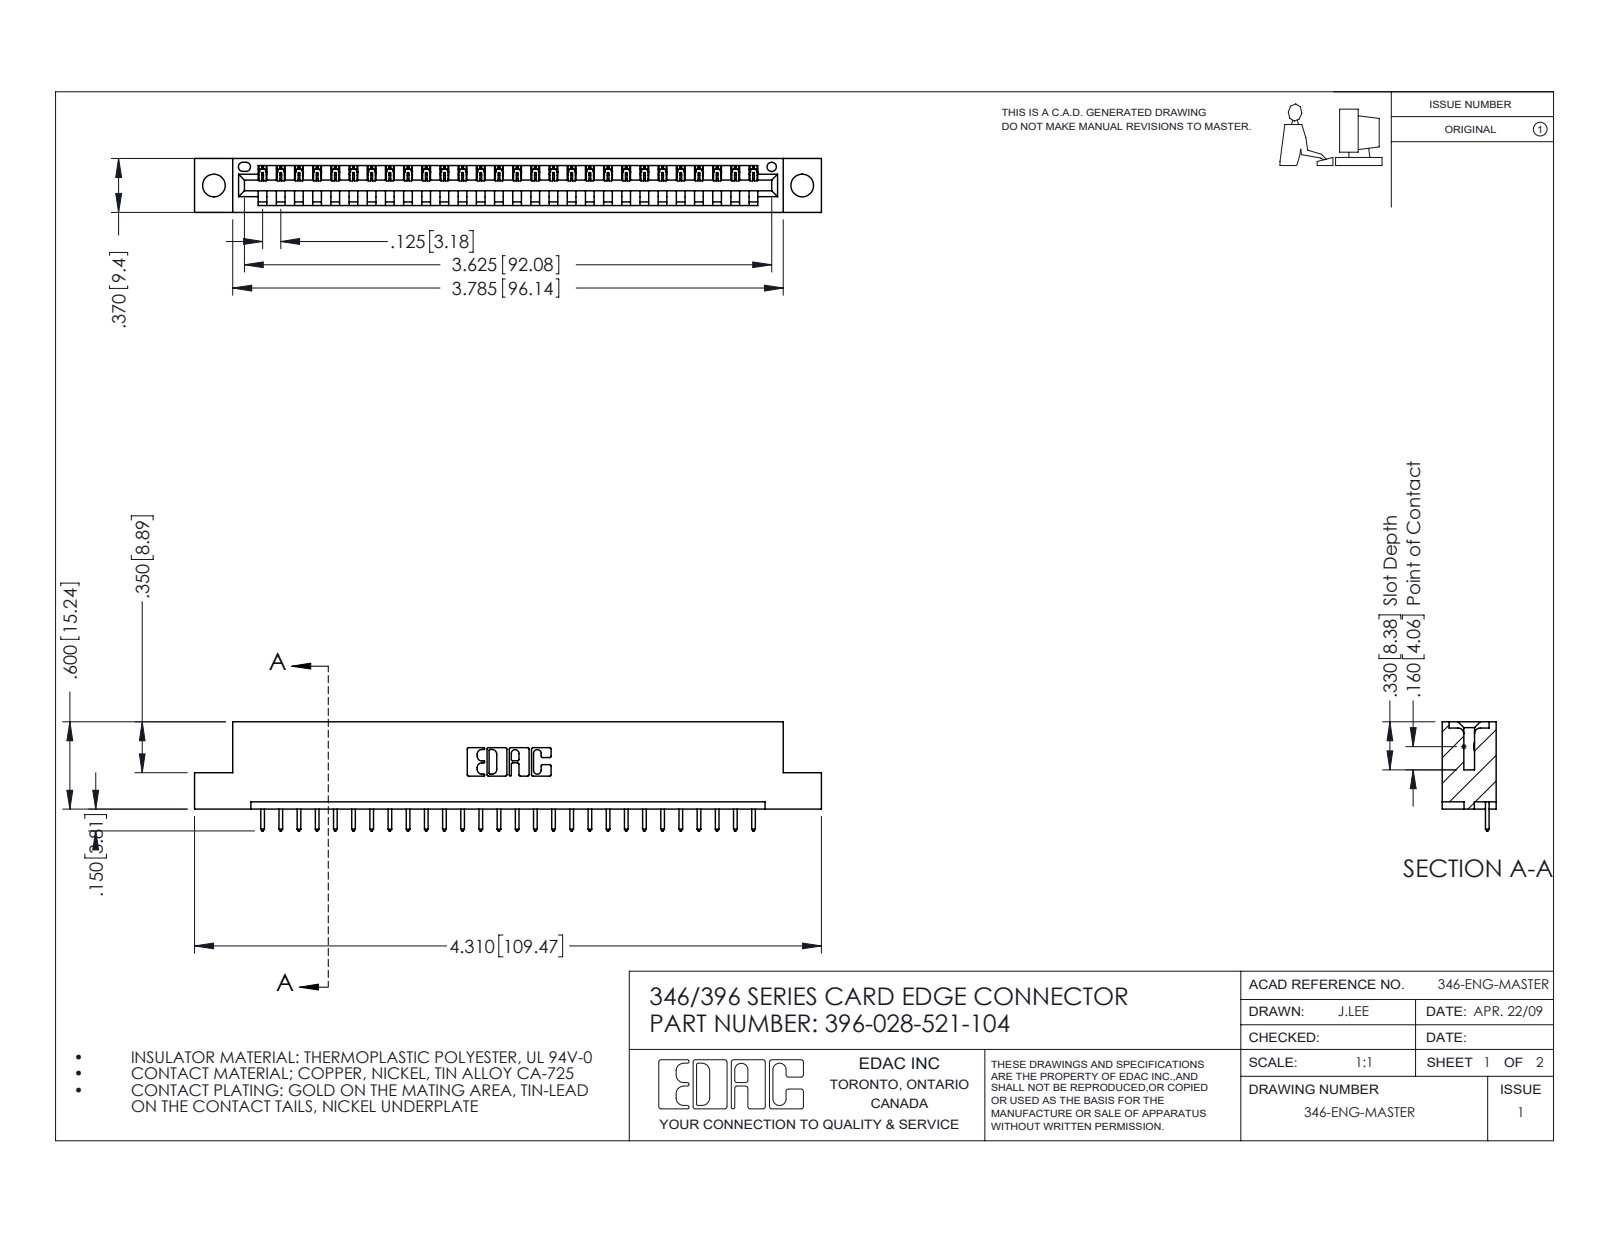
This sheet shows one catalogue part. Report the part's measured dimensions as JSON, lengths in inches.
{"part_name": "346 Part_Flush Mounting Lugs - 0.156 Dia-TH; 396-028-521-104; 345-292-001_345-293-121", "step_written_by": "SolidWorks 2016 (CONFIG_CONTROL_DESIGN)", "units": "inches", "bodies": {"solids": 29, "faces": 1746, "planar": 1196, "cylindrical": 550, "other": 0}, "overall_size": [4.31, 0.75, 0.37], "volume_in3": 0.623, "surface_area_in2": 18.76, "round_holes": [[0.156, 2], [0.064, 1]], "partial_cylinders_radius": [[0.006, 56], [0.01, 56], [0.01, 22], [0.007, 6], [0.031, 6], [0.026, 3], [0.031, 2], [0.04, 2]], "face_to_face_distances": [0.048, 0.322, 0.37, 0.25, 0.072, 0.298, 0.025, 0.148, 0.222, 0.1], "hole_center_spacings": [0.246, 3.837, 4.045]}
